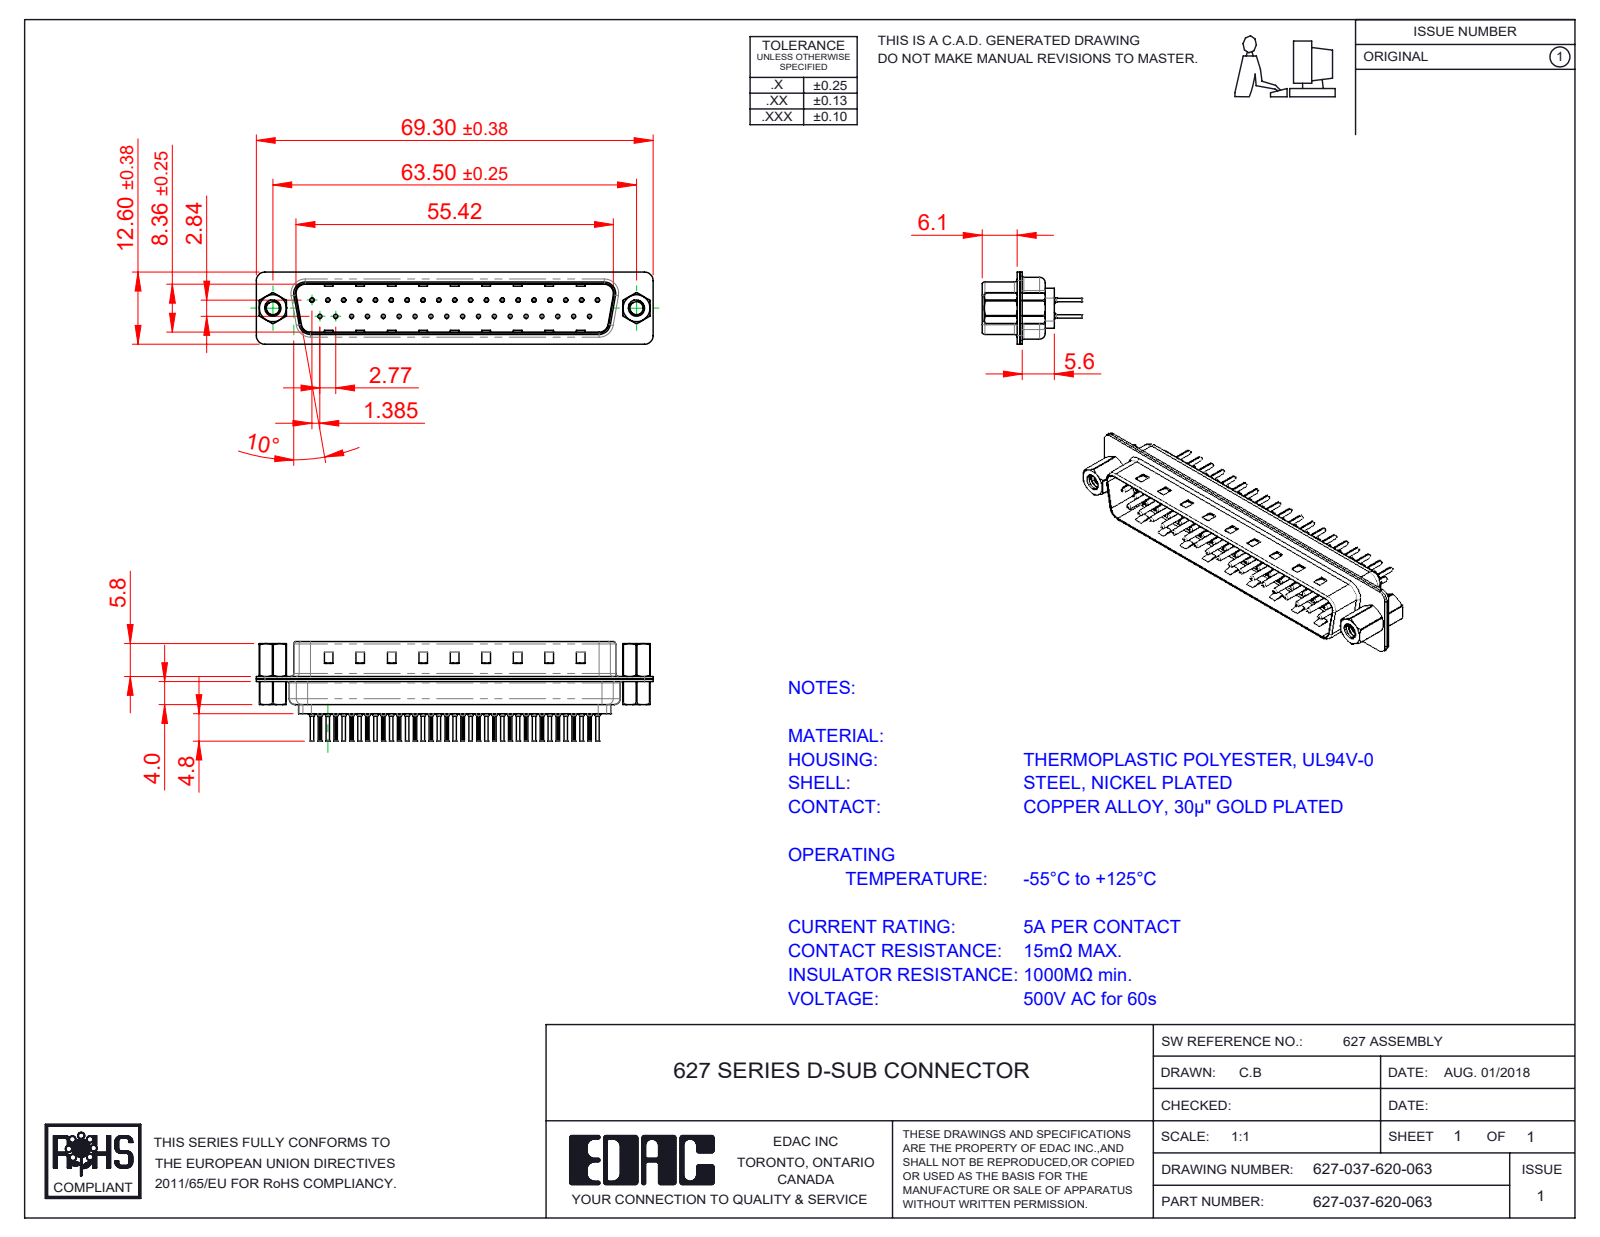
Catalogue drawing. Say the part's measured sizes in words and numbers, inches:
The part is named "627 Contact Row 1_20L; 627 Contact Row 2_20L; 627-037-620-063; 627 Shell Front_37 Contacts (+4 more)". Its 3-D file was written by "SolidWorks 2020 (CONFIG_CONTROL_DESIGN)". It is 44 solids with 4160 faces: 1113 planar, 1580 cylindrical and 1467 other. Overall it measures 2.728 by 0.681 by 0.496 inches. Its volume is 0.239 cubic inches and its surface area 17.29 square inches. Round holes: 37 of diameter 0.008, 37 of diameter 0.014, 37 of diameter 0.043, 37 of diameter 0.063, 2 of diameter 0.089, 2 of diameter 0.09, 2 of diameter 0.157, 2 of diameter 0.189. Round bosses or shafts: 37 of diameter 0.079, 37 of diameter 0.059, 37 of diameter 0.03, 37 of diameter 0.024, 2 of diameter 0.197, 2 of diameter 0.193, 2 of diameter 0.11. Partial cylindrical surfaces (rounded edges, fillets, slot ends): 74 of radius 0.004, 16 of radius 0.059, 12 of radius 0.079, 8 of radius 0.02, 8 of radius 0.063, 4 of radius 0.01, 4 of radius 0.024, 4 of radius 0.026. The main face-to-face distances are 0.016, 0.032, 0.377, 0.018, 0.345, 0.059, 0.035, 0.055, 0.238, 0.256. The hole center spacings are 0.124, 0.109, 0.218, 0.327, 0.198, 0.398, 0.436, 0.503.
